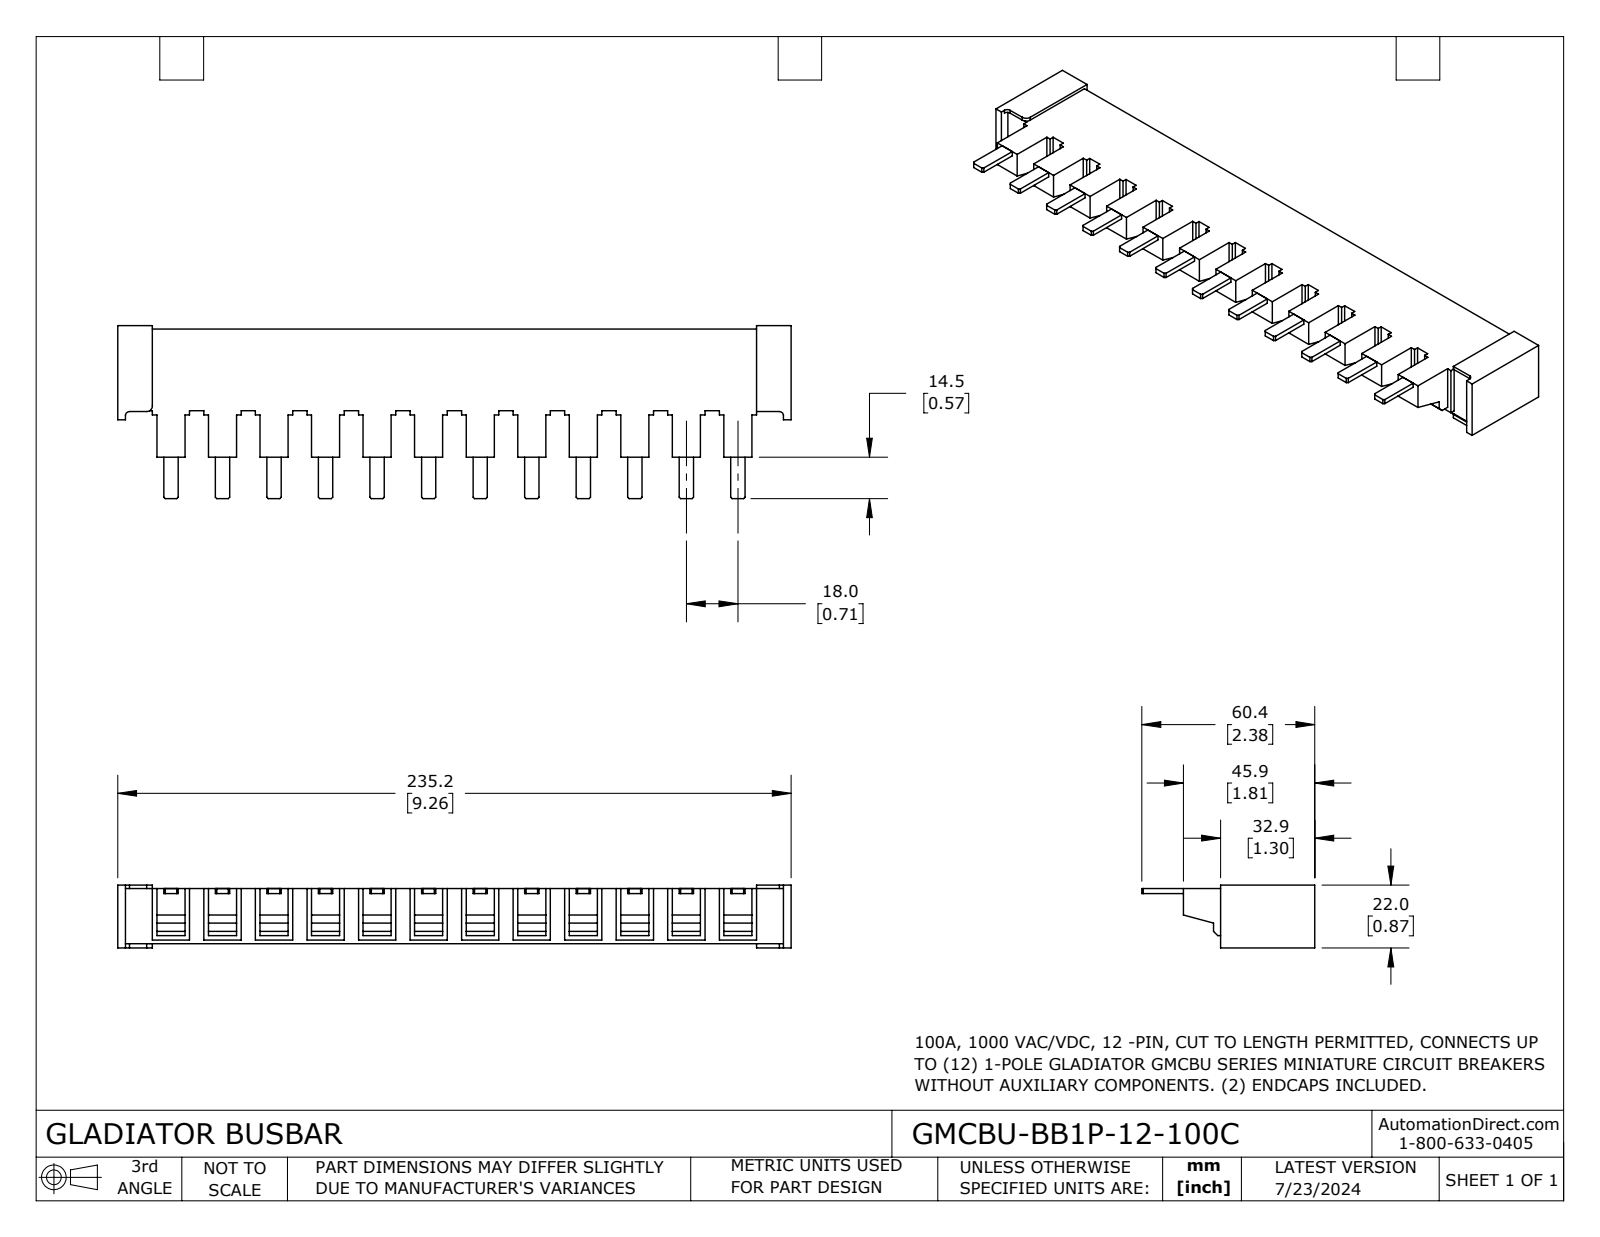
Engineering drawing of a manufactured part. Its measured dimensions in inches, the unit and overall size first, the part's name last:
Units: inches
Overall size (bounding box): 9.26 × 2.378 × 0.866
Partial cylindrical surfaces — rounded edges, fillets, slot ends (radius × count): R0.055 ×2, R0.079 ×1
Main face-to-face distances: 0.76, 0.709, 1.417, 2.126, 0.059, 2.835, 1.122, 3.543, 0.047, 4.252
Volume: 9.716 in³ · Surface area: 54.83 in²
Bodies: 1 solid, 248 faces (242 planar, 6 cylindrical, 0 other)
Part name (STEP PRODUCT): GMCBU-BB1P-12-100C
STEP written by: SolidWorks 2023 (CONFIG_CONTROL_DESIGN)
